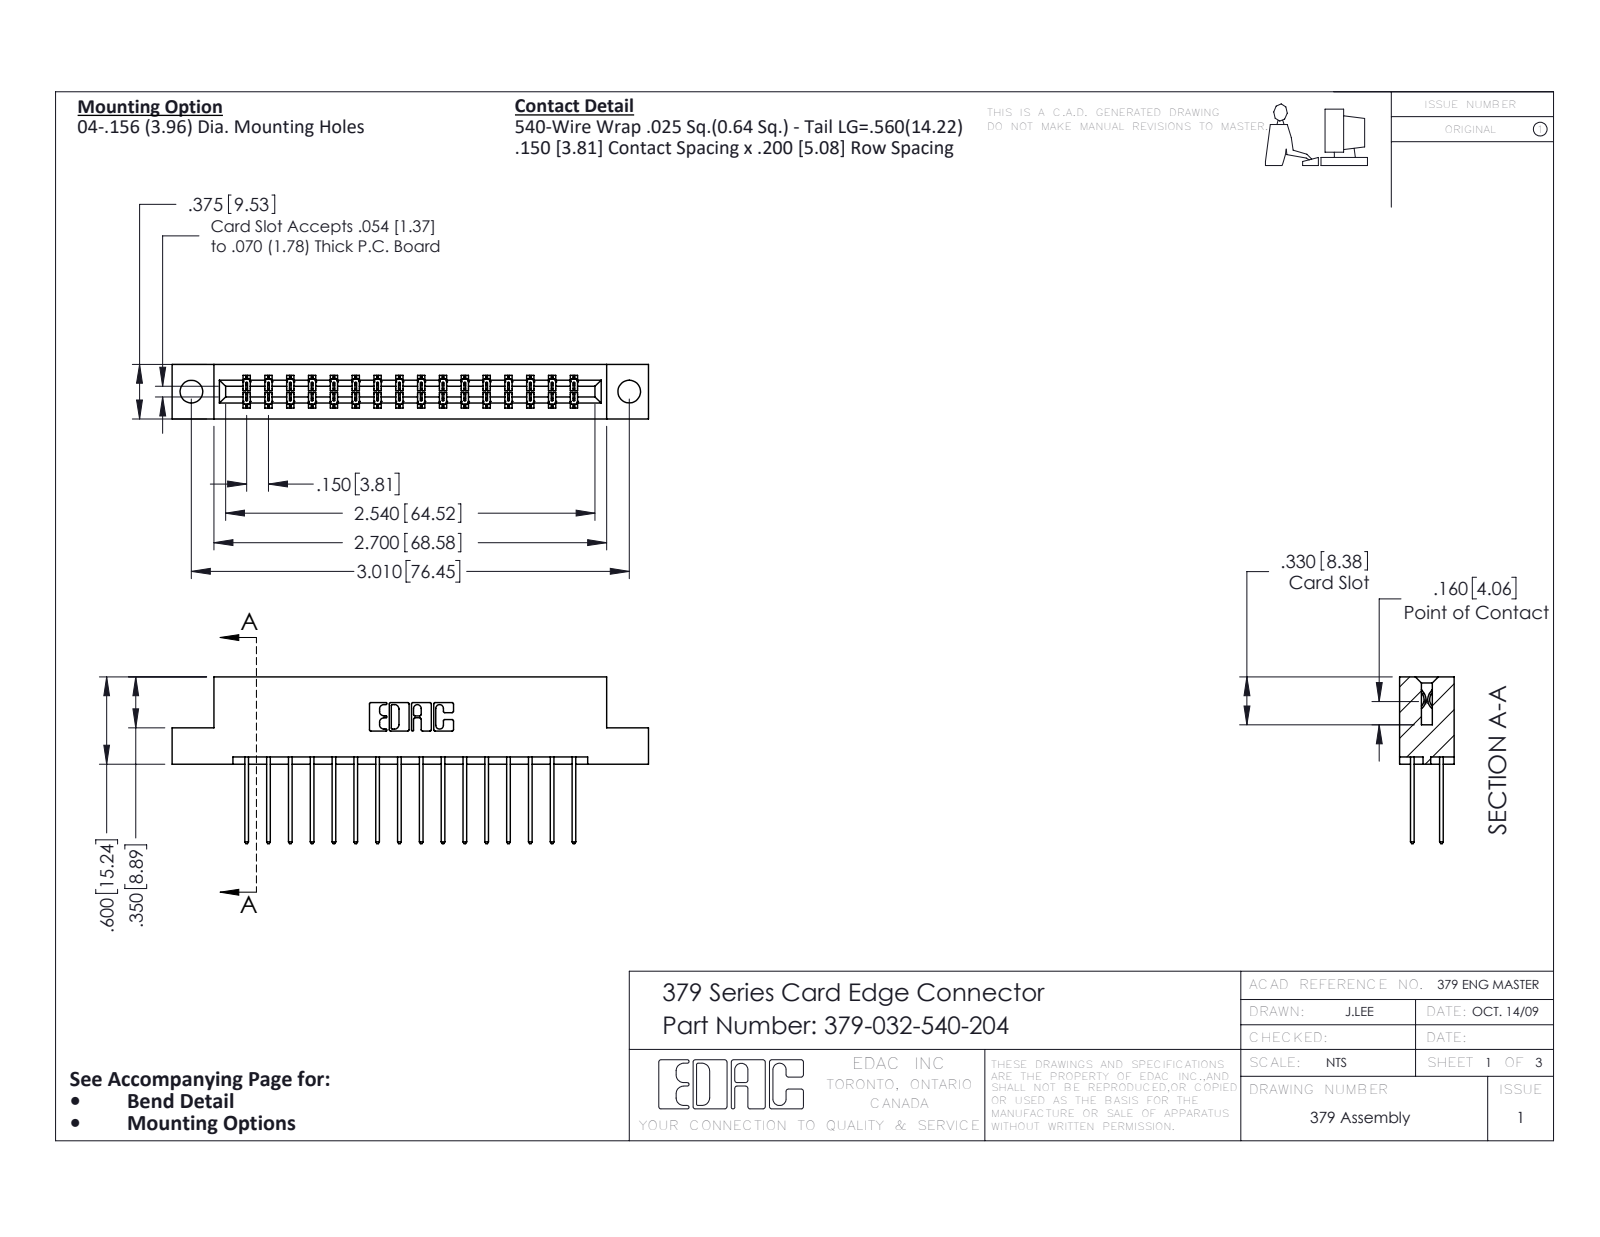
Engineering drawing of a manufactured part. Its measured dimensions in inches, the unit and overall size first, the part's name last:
Units: inches
Overall size (bounding box): 3.275 × 1.147 × 0.375
Round holes (diameter × count): ⌀0.156 ×2
Partial cylindrical surfaces — rounded edges, fillets, slot ends (radius × count): R0.006 ×63, R0.01 ×32, R0.01 ×22, R0.007 ×6, R0.031 ×6, R0.026 ×3, R0.014 ×2, R0.022 ×2
Main face-to-face distances: 0.3, 0.075, 0.2, 0.1, 0.375, 0.275, 0.15, 0.05, 0.6, 0.025
Hole centre spacings: 3.01
Volume: 0.523 in³ · Surface area: 15.16 in²
Bodies: 33 solids, 1778 faces (1222 planar, 556 cylindrical, 0 other)
Part name (STEP PRODUCT): 345-292-001_345-293-140; 379 Part_Flush - .156 Dia - TH; 379-032-540-204
STEP written by: SolidWorks 2020 (CONFIG_CONTROL_DESIGN)
